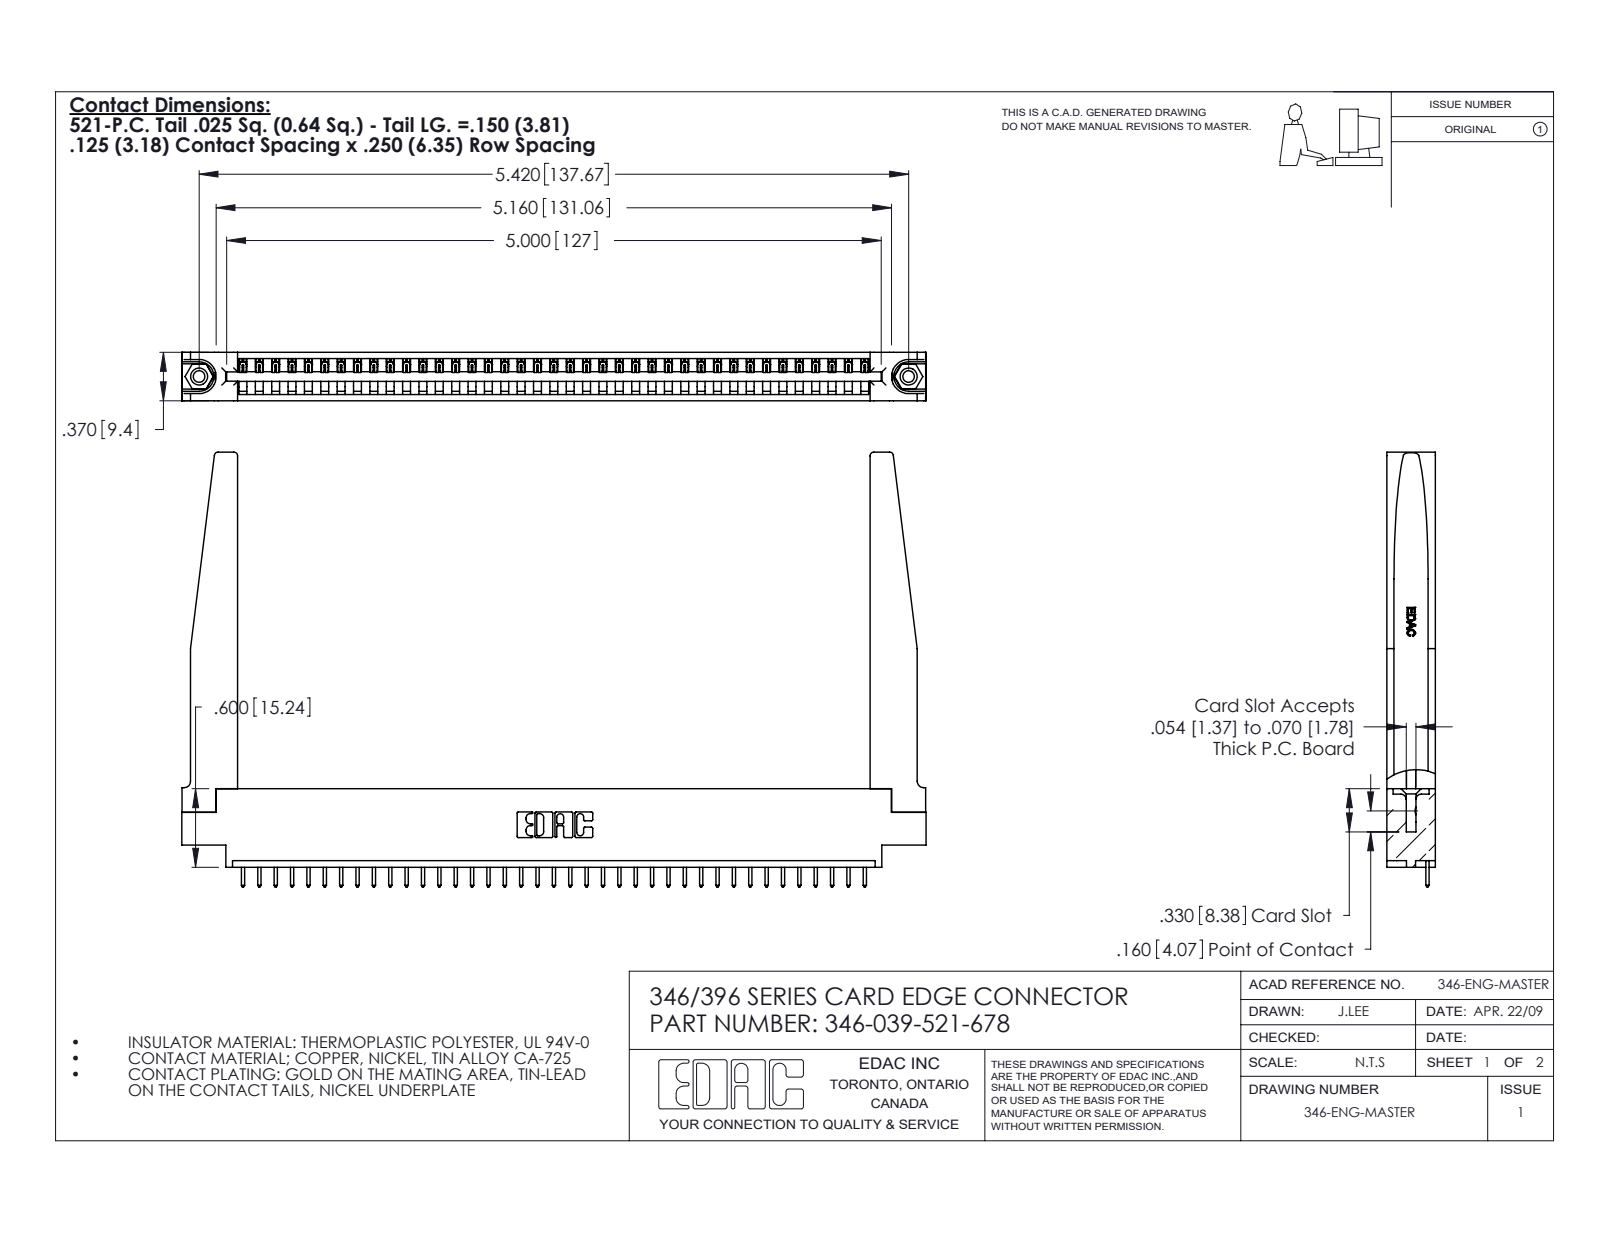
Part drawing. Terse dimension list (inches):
name: 345-292-001_345-293-121; 346-220-078_345-220-078; 346-039-521-678; 345-250-001_345-250-001-102 (+1 more)
written by: SolidWorks 2020 (CONFIG_CONTROL_DESIGN)
unit: in
bodies: 44 solids, 2636 faces (1796 planar, 788 cylindrical, 52 other)
size: 5.685 × 3.32 × 0.37
volume: 1.247 in³; area: 35.89 in²
holes: 2× ⌀0.089, 2× ⌀0.125, 2× ⌀0.156, 1× ⌀0.064
bosses: 2× ⌀0.155
rounds: 78× R0.006, 78× R0.01, 22× R0.01, 8× R0.03, 6× R0.007, 6× R0.031, 3× R0.026, 2× R0.031
face distances: 0.37, 0.048, 0.322, 0.072, 0.148, 0.15, 0.25, 0.298, 0.025, 0.222
hole spacings: 0.246, 5.211, 5.42
